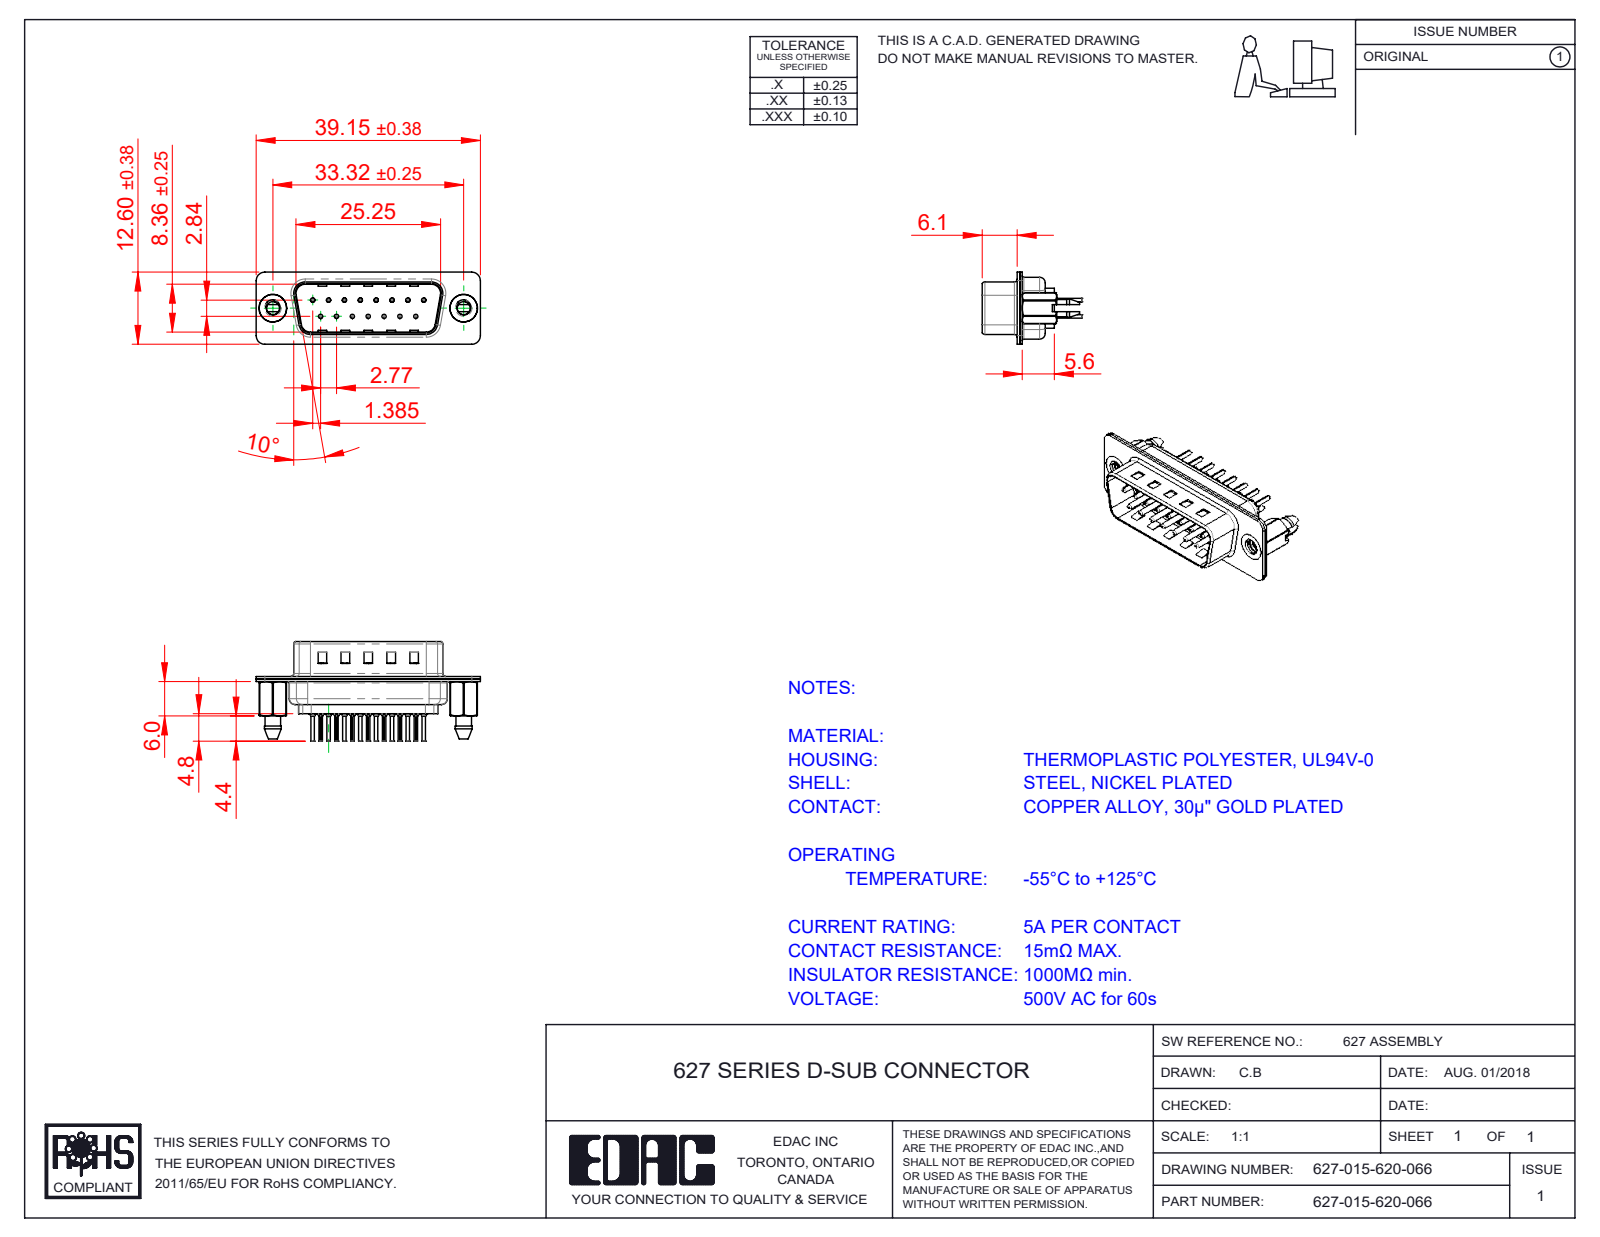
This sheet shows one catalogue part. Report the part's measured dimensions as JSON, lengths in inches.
{"part_name": "627 Shell Rear_15 Contacts; 627 Shell Front_15 Contacts; 627 Contact Row 2_20L; 627-015-620-066 (+3 more)", "step_written_by": "SolidWorks 2020 (CONFIG_CONTROL_DESIGN)", "units": "inches", "bodies": {"solids": 20, "faces": 1884, "planar": 531, "cylindrical": 720, "other": 633}, "overall_size": [1.541, 0.681, 0.496], "volume_in3": 0.119, "surface_area_in2": 8.81, "round_holes": [[0.008, 15], [0.014, 15], [0.043, 15], [0.063, 15], [0.089, 2], [0.157, 2], [0.189, 2]], "round_bosses_or_shafts": [[0.079, 15], [0.059, 15], [0.03, 15], [0.024, 15], [0.193, 2]], "partial_cylinders_radius": [[0.004, 30], [0.059, 18], [0.079, 12], [0.063, 10], [0.02, 8], [0.01, 4], [0.024, 4], [0.026, 4]], "face_to_face_distances": [0.016, 0.018, 0.035, 0.032, 0.377, 0.345, 0.059, 0.055, 0.256, 0.22], "hole_center_spacings": [0.124, 0.109, 0.218, 0.327, 0.436, 0.198, 0.198, 0.294]}
